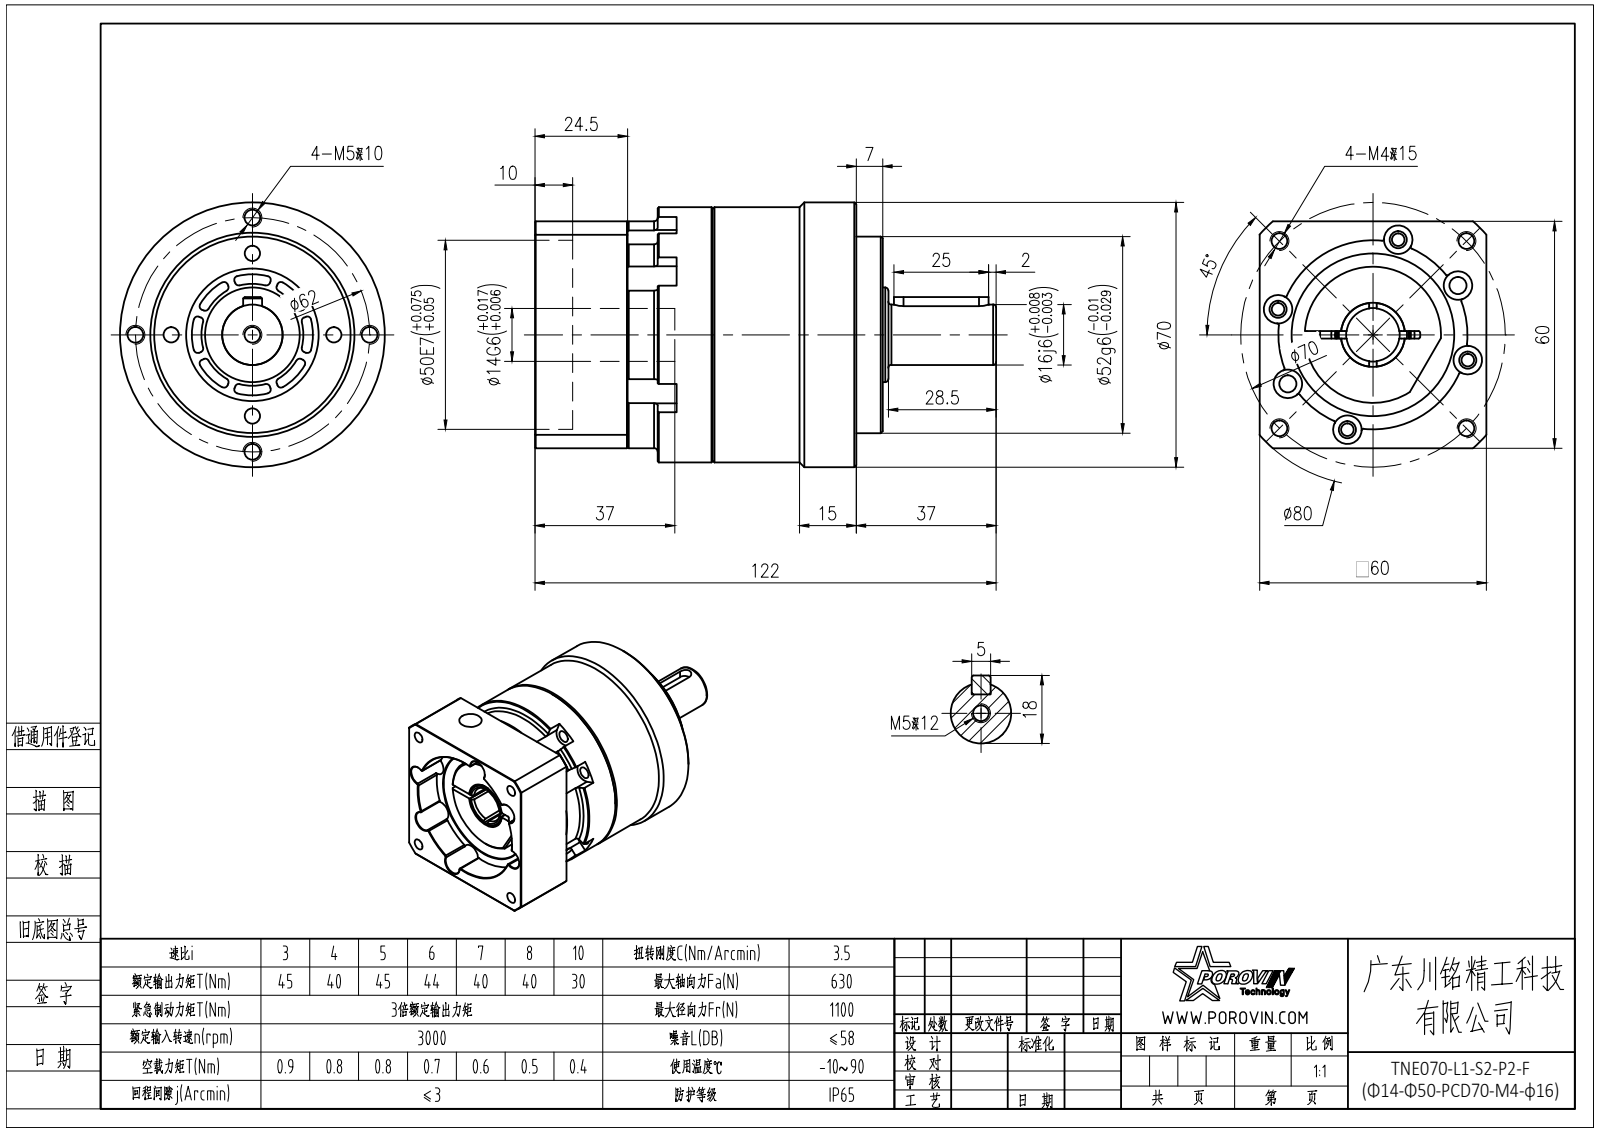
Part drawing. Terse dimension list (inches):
name: hexagon socket head cap screws gb_GB_FASTENER_SCREWS_HSHCS M4X16-N; spring lock washers--normal type gb_GB_FASTENER_WASHER_SW 4; hexagon socket head cap screws gb_GB_FASTENER_SCREWS_HSHCS M4X20-N; hex socket set screws with flat point gb_GB_FASTENER_SCREWS_HSFP M10X10-N (+2 more)
written by: SolidWorks 2016 (CONFIG_CONTROL_DESIGN)
unit: in
bodies: 32 solids, 1045 faces (387 planar, 392 cylindrical, 266 other)
size: 4.803 × 2.756 × 2.756
volume: 15.72 in³; area: 102.5 in²
holes: 12× ⌀0.173, 12× ⌀0.177, 10× ⌀0.13, 6× ⌀0.165, 6× ⌀0.295, 4× ⌀0.157, 2× ⌀0.217, 1× ⌀0.335, 1× ⌀0.551, 1× ⌀0.559, 1× ⌀0.984, 1× ⌀1.378
bosses: 12× ⌀0.276, 12× ⌀0.26, 12× ⌀0.157, 1× ⌀2.756, 1× ⌀2.657, 1× ⌀2.047, 1× ⌀1.417, 1× ⌀0.886
rounds: 36× R0.02, 32× R0.039, 6× R0.148, 2× R0.098, 1× R0.187, 1× R0.531, 1× R0.63, 1× R1.181
face distances: 0.197, 0.886, 2.362, 1.496, 0.433, 1.083, 1.142, 0.079, 1.299, 2.382
hole spacings: 2.402, 0.983, 1.005, 1.485, 2.065, 0.339, 1.024, 1.201
